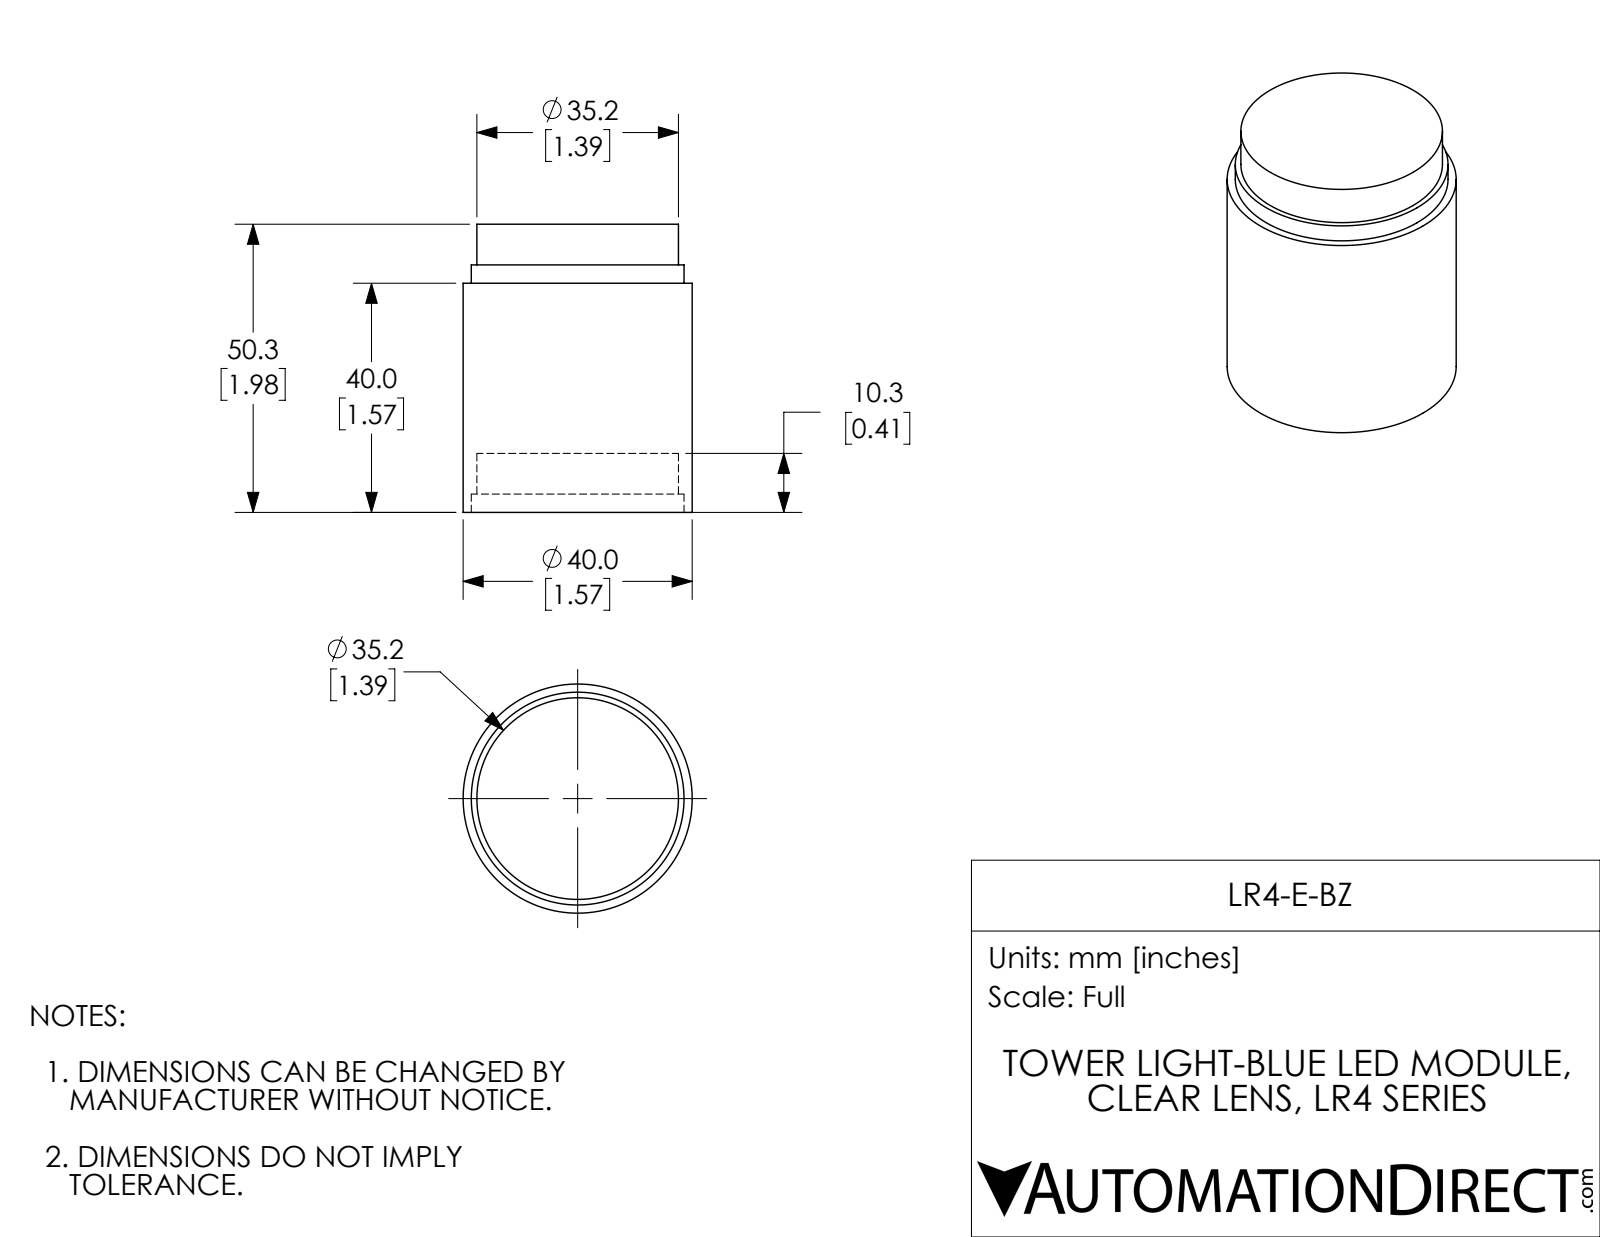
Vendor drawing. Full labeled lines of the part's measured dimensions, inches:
Part name (STEP PRODUCT): LR4-E-BZ
STEP written by: SolidWorks 2017 (AUTOMOTIVE_DESIGN)
Units: inches
Bodies: 1 solid, 16 faces (6 planar, 10 cylindrical, 0 other)
Overall size (bounding box): 1.98 × 1.575 × 1.575
Volume: 3.067 in³ · Surface area: 15.28 in²
Round holes (diameter × count): ⌀1.386 ×1, ⌀1.463 ×1
Round bosses / shafts (diameter × count): ⌀1.575 ×1
Main face-to-face distances: 1.575, 0.406, 0.126, 0.28, 1.98, 1.169, 1.701, 1.295, 1.449, 1.854
